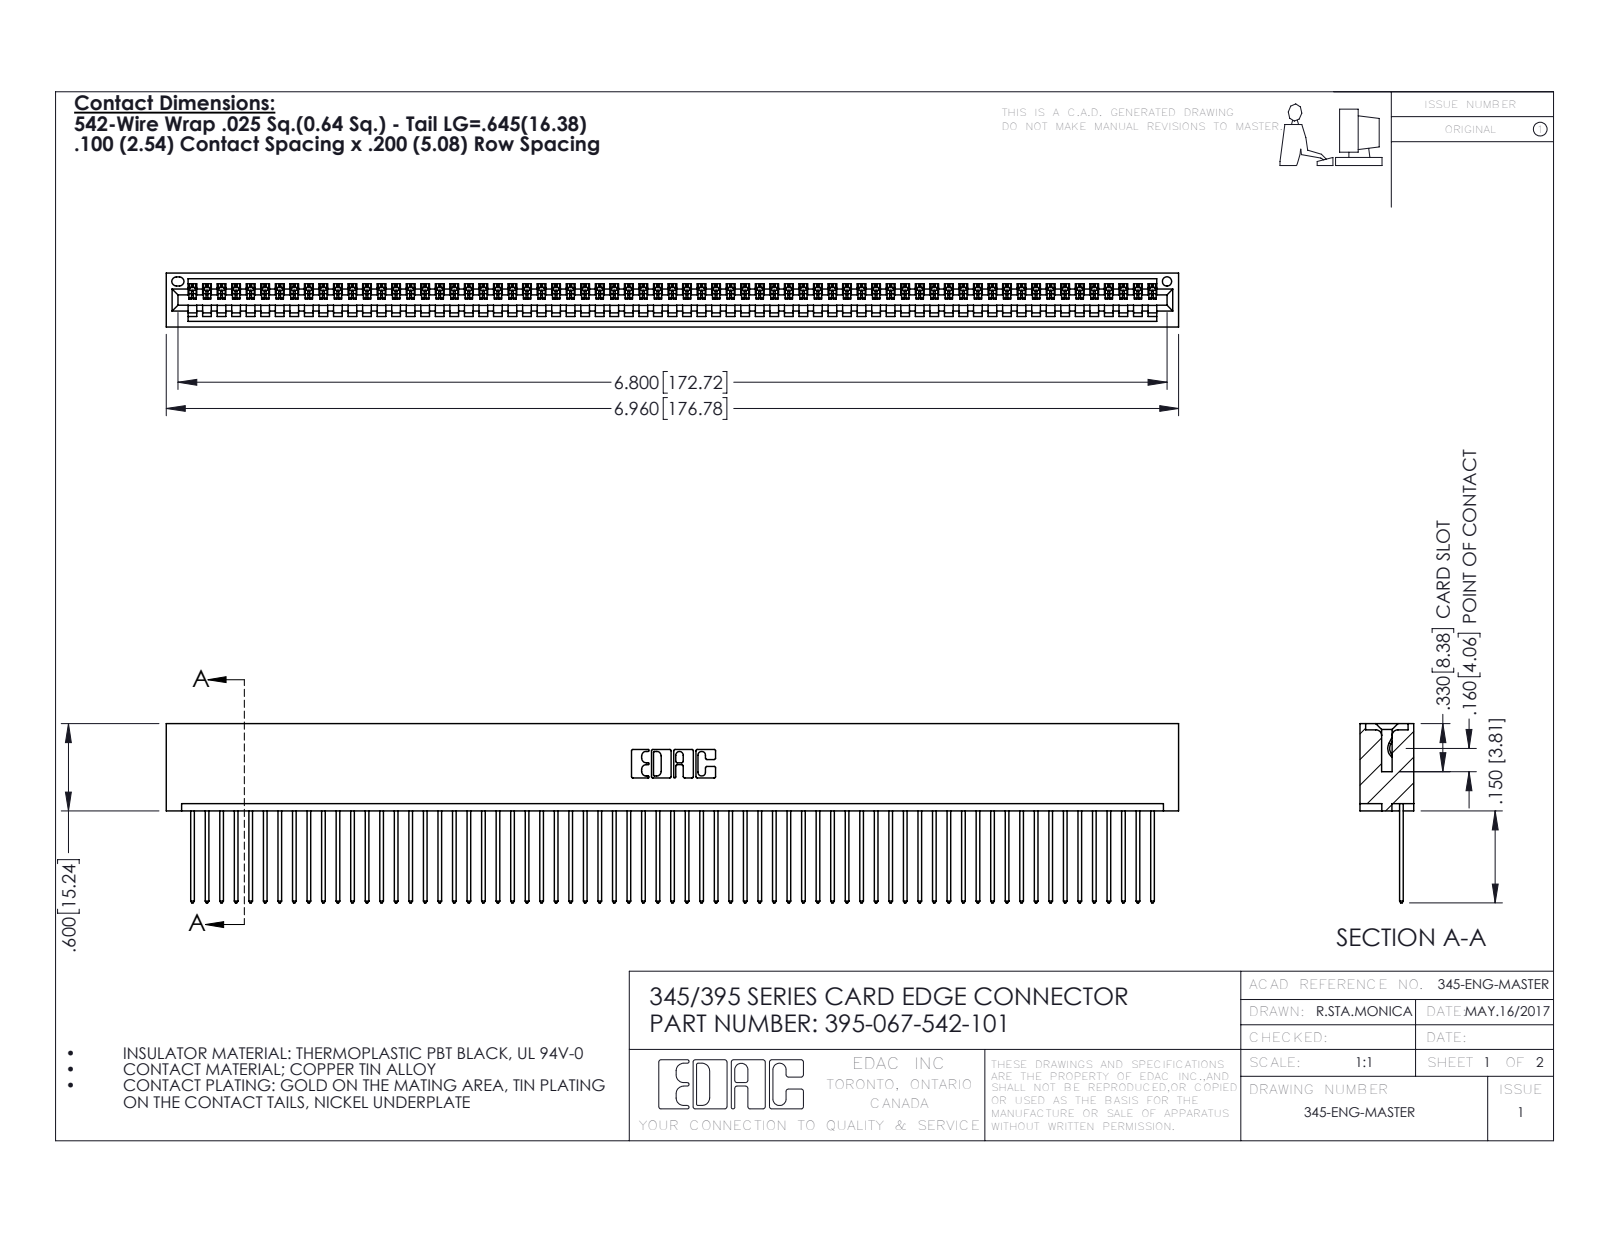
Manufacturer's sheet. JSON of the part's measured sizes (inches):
{"part_name": "345 Part_No Mounting Lugs; 395-067-542-101; 345-292-001_345-293-142", "step_written_by": "SolidWorks 2016 (CONFIG_CONTROL_DESIGN)", "units": "inches", "bodies": {"solids": 68, "faces": 4004, "planar": 2756, "cylindrical": 1248, "other": 0}, "overall_size": [6.96, 1.232, 0.37], "volume_in3": 1.082, "surface_area_in2": 38.8, "round_holes": [[0.064, 1]], "partial_cylinders_radius": [[0.006, 134], [0.01, 134], [0.01, 22], [0.007, 6], [0.031, 6], [0.026, 3], [0.031, 2], [0.04, 2]], "face_to_face_distances": [0.072, 0.298, 0.098, 0.272, 0.025, 0.37, 0.2, 0.225, 0.149, 0.072]}
